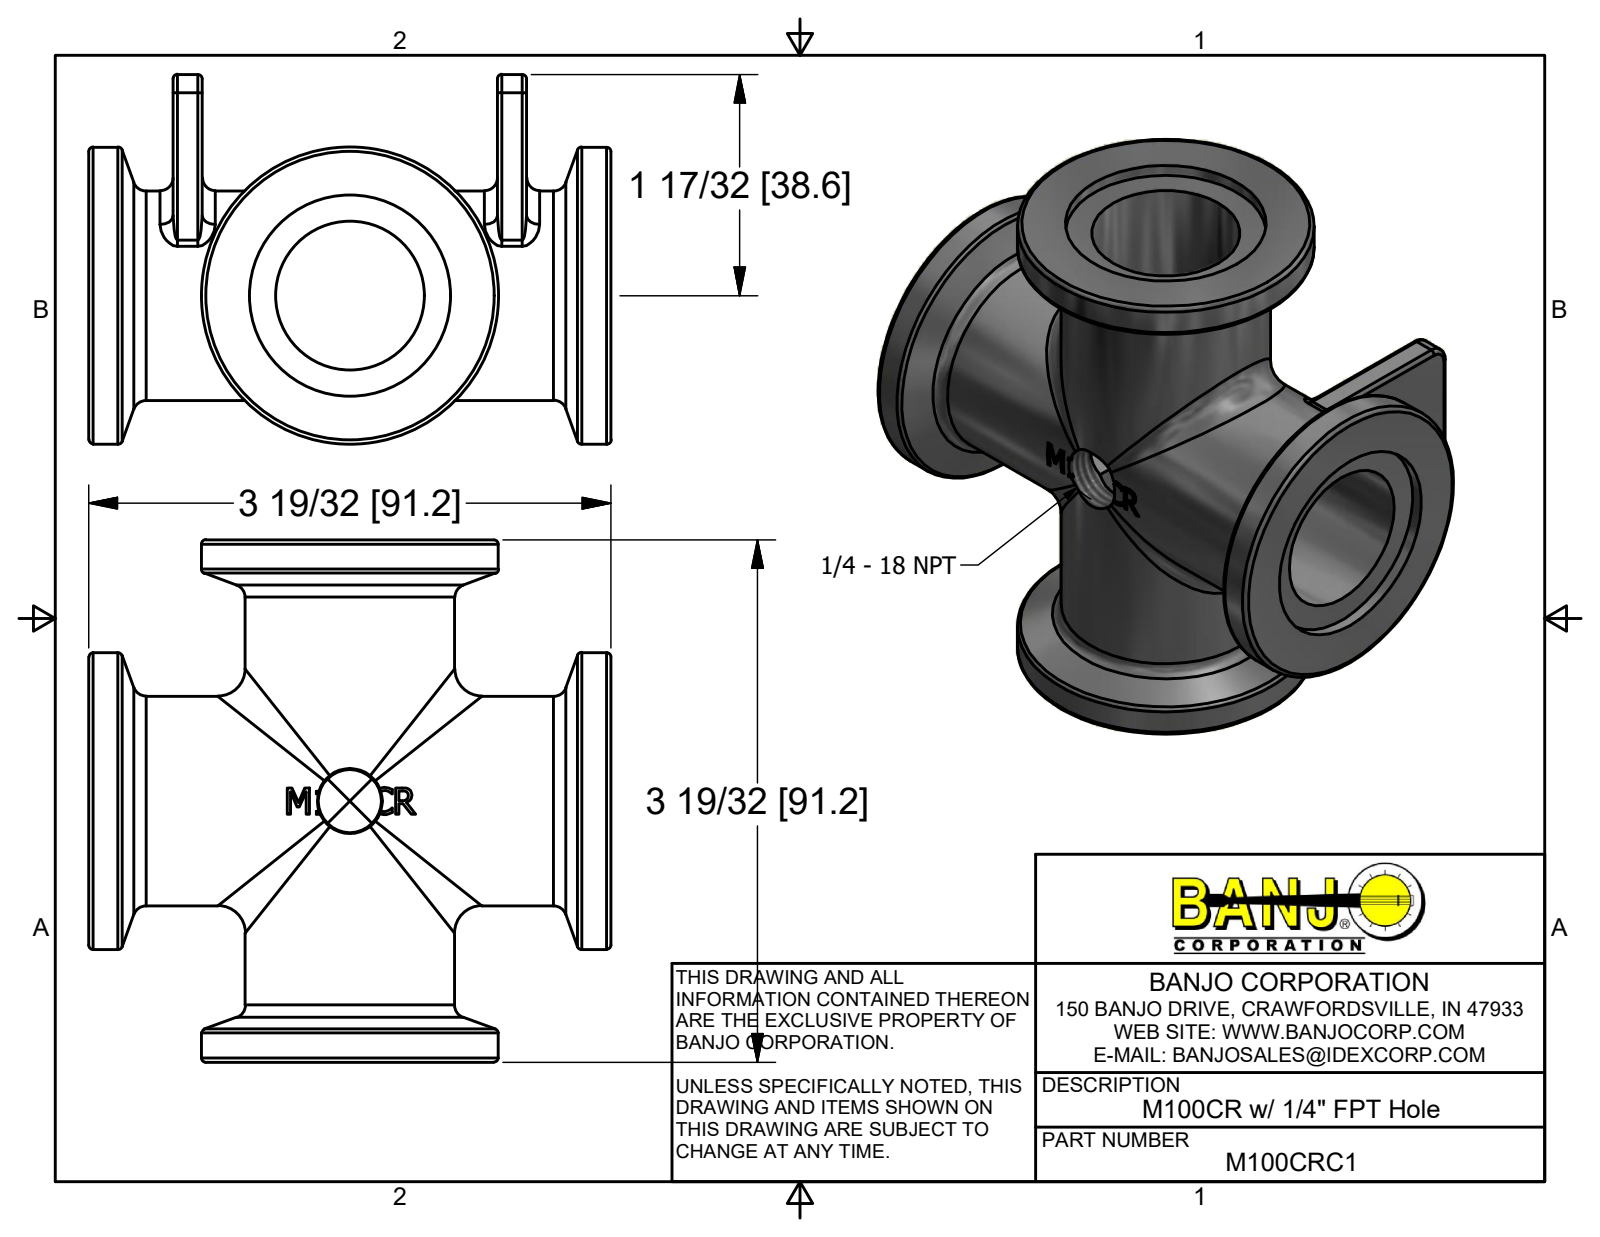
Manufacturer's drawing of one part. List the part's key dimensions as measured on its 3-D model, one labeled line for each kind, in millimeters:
Part name (STEP PRODUCT): M100CRC1; M100CRU
STEP written by: Autodesk Inventor 2017 (AUTOMOTIVE_DESIGN)
Units: millimetres
Bodies: 1 solid, 376 faces (148 planar, 76 cylindrical, 152 other)
Overall size (bounding box): 91.19 × 91.19 × 64.52
Volume: 107 587 mm³ · Surface area: 41 320 mm²
Round holes (diameter × count): ⌀25.91 ×2, ⌀35.05 ×2
Round bosses / shafts (diameter × count): ⌀51.82 ×2, ⌀36.58 ×2
Partial cylindrical surfaces — rounded edges, fillets, slot ends (radius × count): R0.76 ×12, R2.29 ×2, R3.17 ×2, R17.78 ×1
Main face-to-face distances: 91.18, 2.13, 89.05, 14.73, 19.81, 71.37, 76.45, 56.64, 5.08, 86.92
